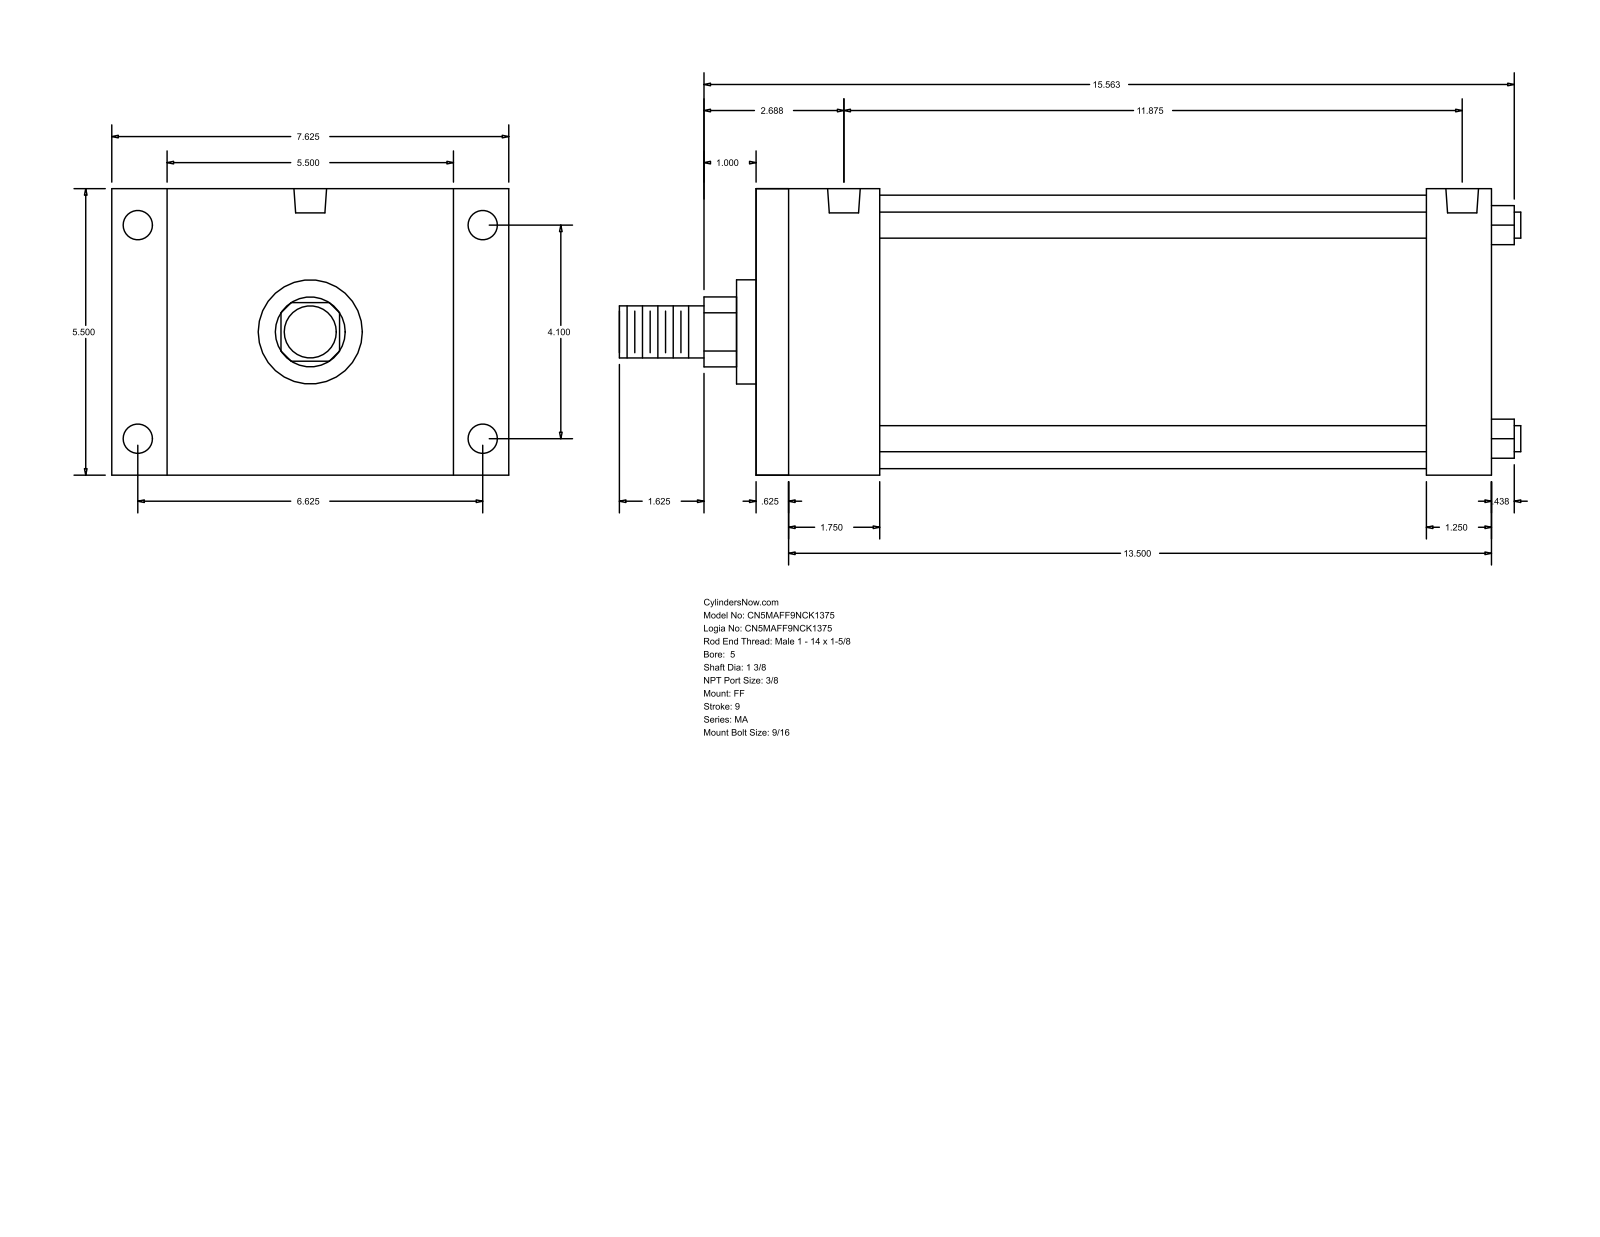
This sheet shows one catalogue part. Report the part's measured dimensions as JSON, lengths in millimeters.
{"part_name": "MA_FF__0500_1.375", "step_written_by": "GSSL Pune (CONFIG_CONTROL_DESIGN)", "units": "millimeters", "bodies": {"solids": 0, "faces": 92, "planar": 64, "cylindrical": 28, "other": 0}, "overall_size": [439.74, 193.68, 139.7], "round_holes": [[11.11, 4], [14.29, 4], [15.93, 2]], "round_bosses_or_shafts": [[12.7, 4], [133.35, 1], [50.8, 1], [34.92, 1], [25.4, 1]], "partial_cylinders_radius": [[17.06, 1]], "face_to_face_distances": [139.7, 358.78, 15.87, 342.91, 327.03, 311.16, 31.75, 60.32, 44.45, 266.71], "hole_center_spacings": [4.77, 104.14, 168.28, 197.9, 292.09, 296.86, 301.63]}
